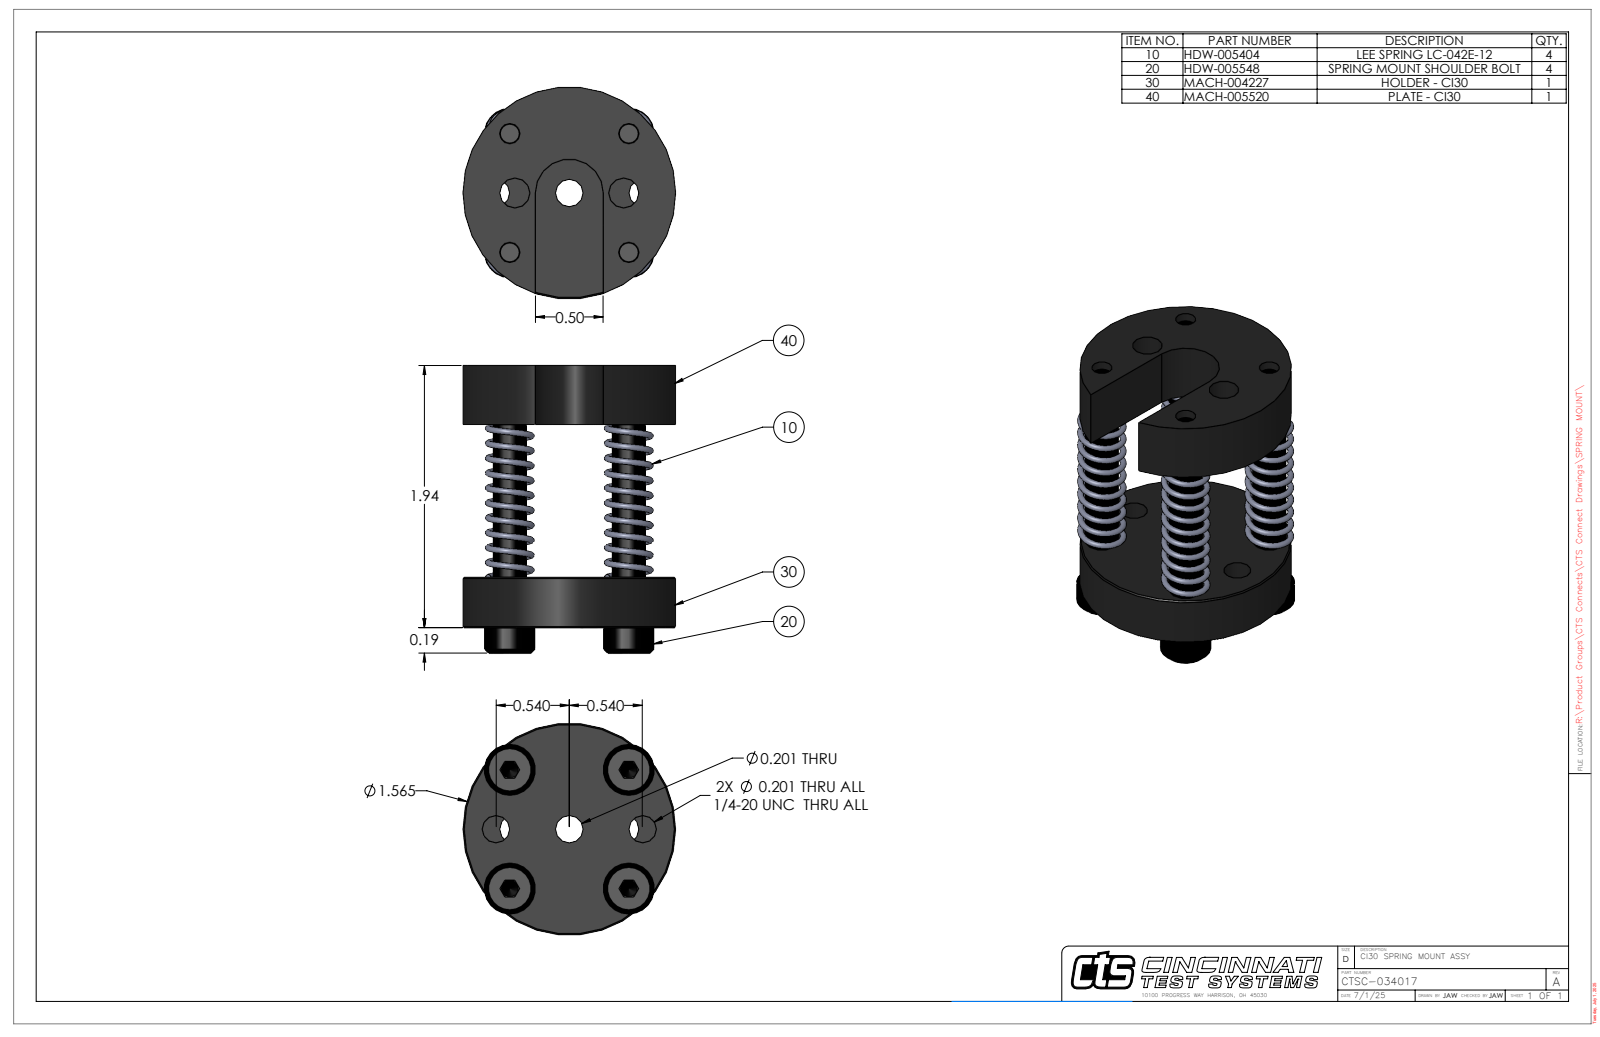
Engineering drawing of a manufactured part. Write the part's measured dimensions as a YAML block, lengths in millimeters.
part_name: "HDW-005548 (.25 X 1.5 SHSS)_SHSSCREW 0.25x1.5-N; MACH-004227 (HOLDER - CI30 REV1); CTSC-034017 (CI30 SPRING MOUNT); HDW-005404 (LEE SPRING LC-042E-12) (+1 more)"
step_written_by: "SolidWorks 2023 (AUTOMOTIVE_DESIGN)"
units: millimeters
bodies: {solids: 10, faces: 226, planar: 86, cylindrical: 72, other: 68}
overall_size: [54, 39.8, 39.8]
volume: 26780
surface_area: 17220
round_holes:
  - {diameter: 3.8, count: 4}
  - {diameter: 6.4, count: 4}
  - {diameter: 5.1, count: 3}
  - {diameter: 5.6, count: 2}
round_bosses_or_shafts:
  - {diameter: 9.5, count: 4}
  - {diameter: 6.3, count: 4}
  - {diameter: 5.8, count: 4}
  - {diameter: 4.8, count: 4}
  - {diameter: 3.4, count: 4}
  - {diameter: 39.8, count: 1}
partial_cylinders:
  - {radius: 6.4, count: 1}
face_to_face_distances: [9.5, 38.1, 28.6, 11.1, 39.7, 49.2, 12.7, 54, 42.9, 14.3]
hole_center_spacings: [11.2, 11.4, 15.7, 22.2, 24, 27.2, 3.6, 10.2]
